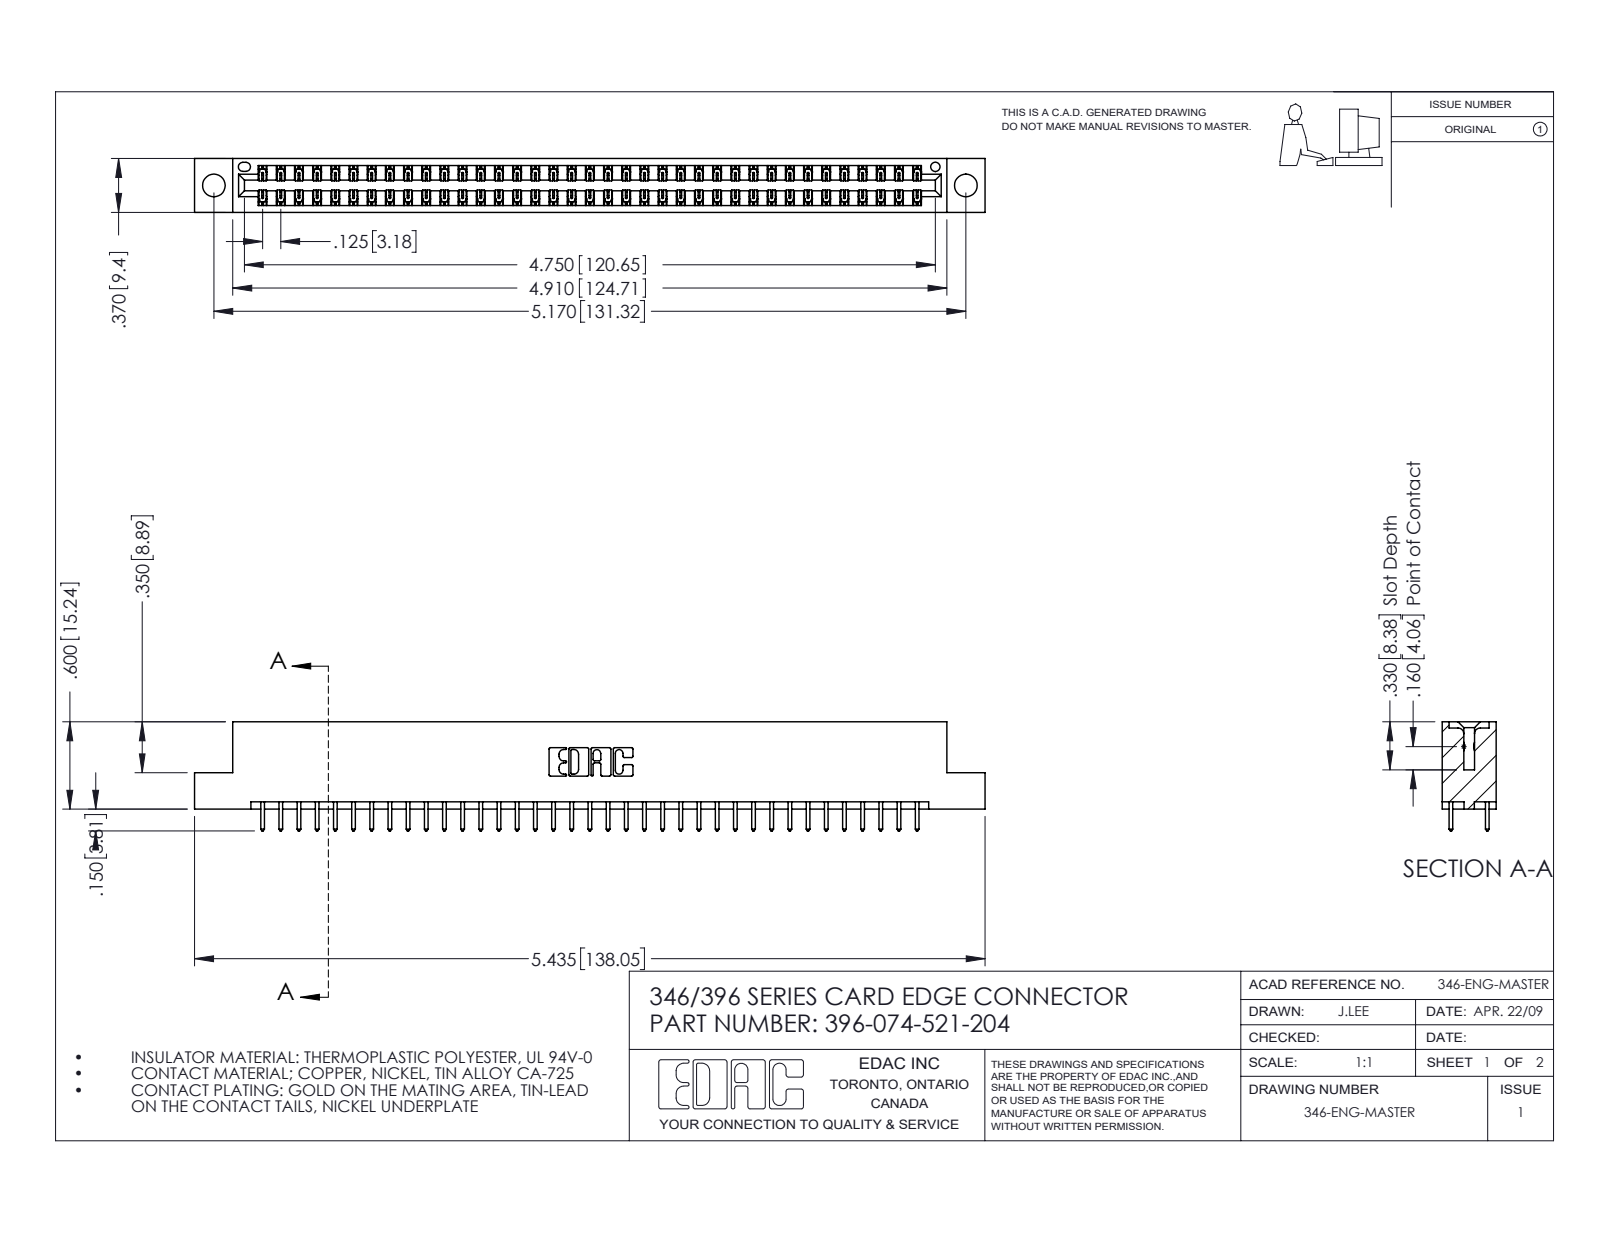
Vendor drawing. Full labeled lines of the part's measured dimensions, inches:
Part name (STEP PRODUCT): 345-292-001_345-293-121; 346 Part_Flush Mounting Lugs - 0.156 Dia-TH; 396-074-521-204
STEP written by: SolidWorks 2016 (CONFIG_CONTROL_DESIGN)
Units: inches
Bodies: 75 solids, 3970 faces (2666 planar, 1304 cylindrical, 0 other)
Overall size (bounding box): 5.435 × 0.75 × 0.37
Volume: 0.812 in³ · Surface area: 27.62 in²
Round holes (diameter × count): ⌀0.156 ×2, ⌀0.064 ×1
Partial cylindrical surfaces — rounded edges, fillets, slot ends (radius × count): R0.006 ×111, R0.01 ×74, R0.01 ×22, R0.007 ×6, R0.031 ×6, R0.026 ×3, R0.014 ×2, R0.022 ×2
Main face-to-face distances: 0.048, 0.322, 0.25, 0.37, 0.072, 0.298, 0.025, 0.275, 0.148, 0.222
Hole centre spacings: 0.246, 4.961, 5.17
